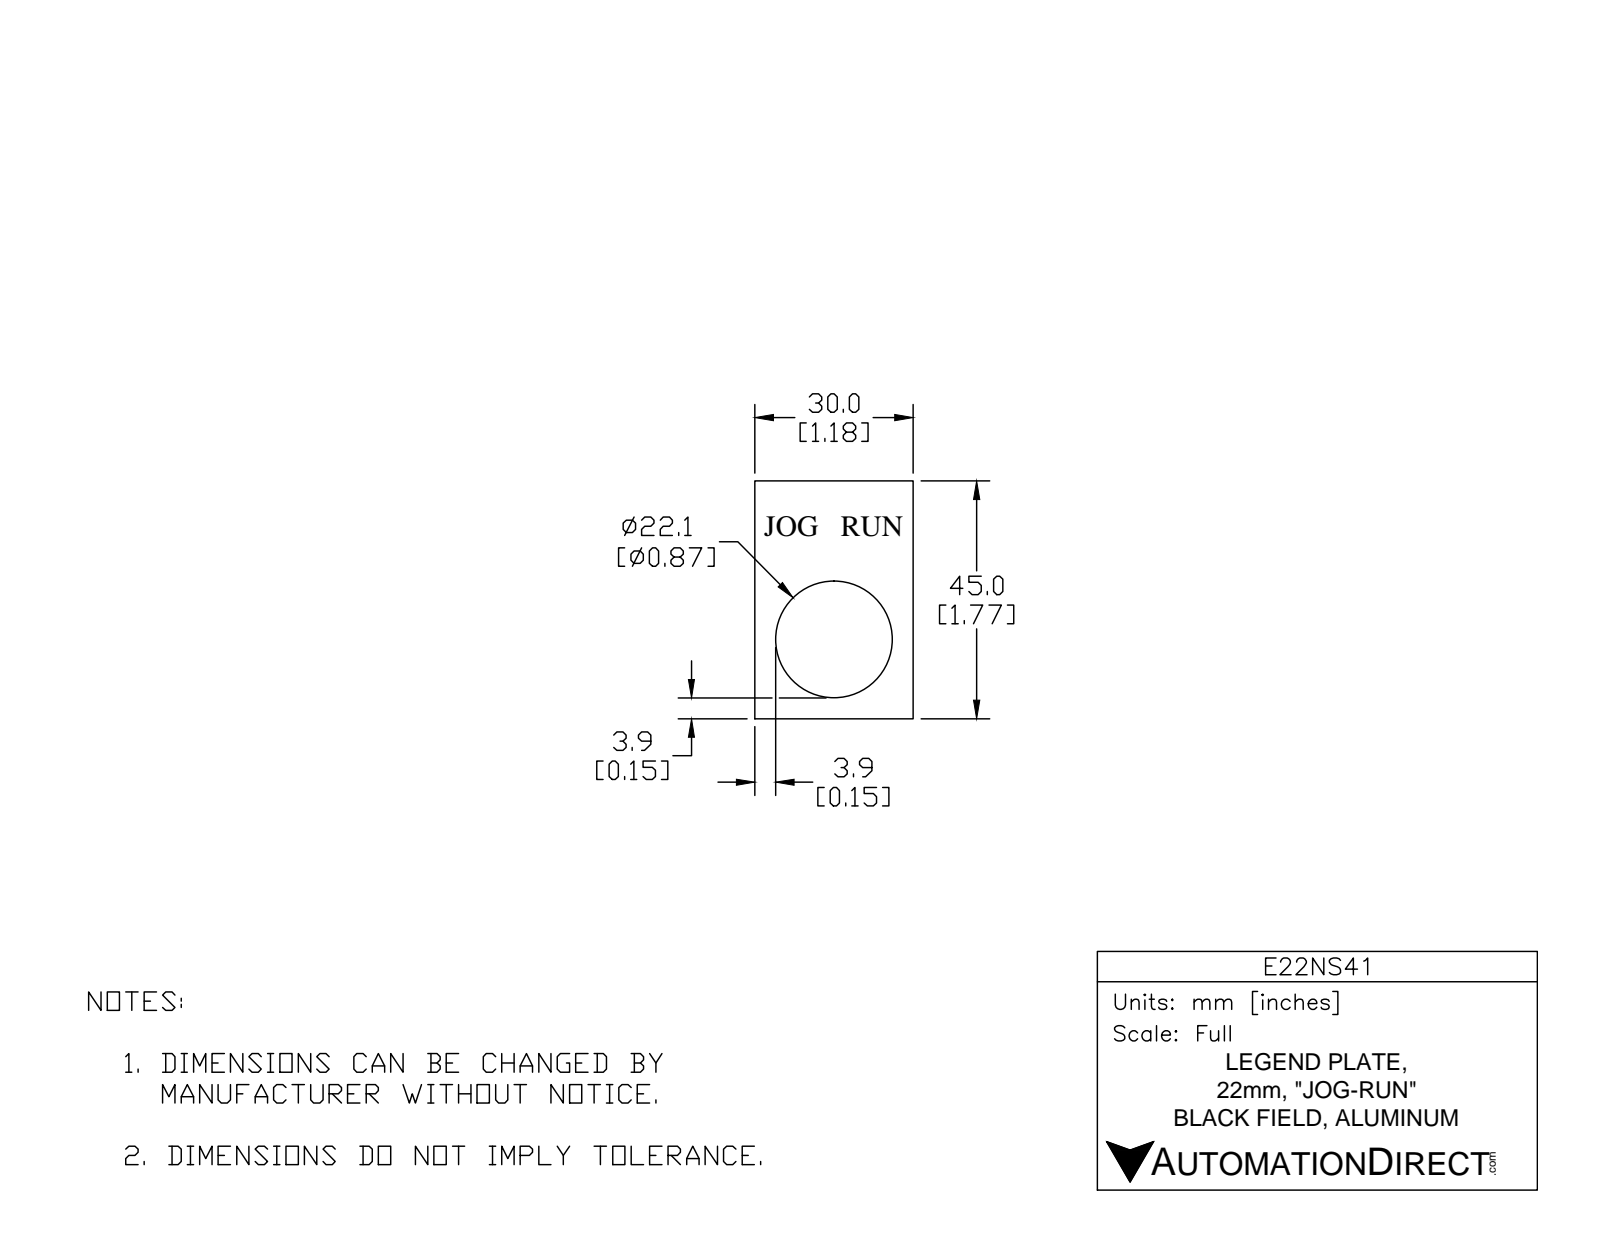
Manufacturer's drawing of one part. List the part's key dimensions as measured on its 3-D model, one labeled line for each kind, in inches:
Part name (STEP PRODUCT): E22NS41
STEP written by: SolidWorks 2017 (AUTOMOTIVE_DESIGN)
Units: inches
Bodies: 1 solid, 94 faces (57 planar, 3 cylindrical, 34 other)
Overall size (bounding box): 1.772 × 1.181 × 0.051
Volume: 0.076 in³ · Surface area: 3.478 in²
Round holes (diameter × count): ⌀0.874 ×1
Main face-to-face distances: 0.051, 1.181, 1.772, 0.041, 0.185, 1.587, 0.528, 0.654, 0.085, 0.112
